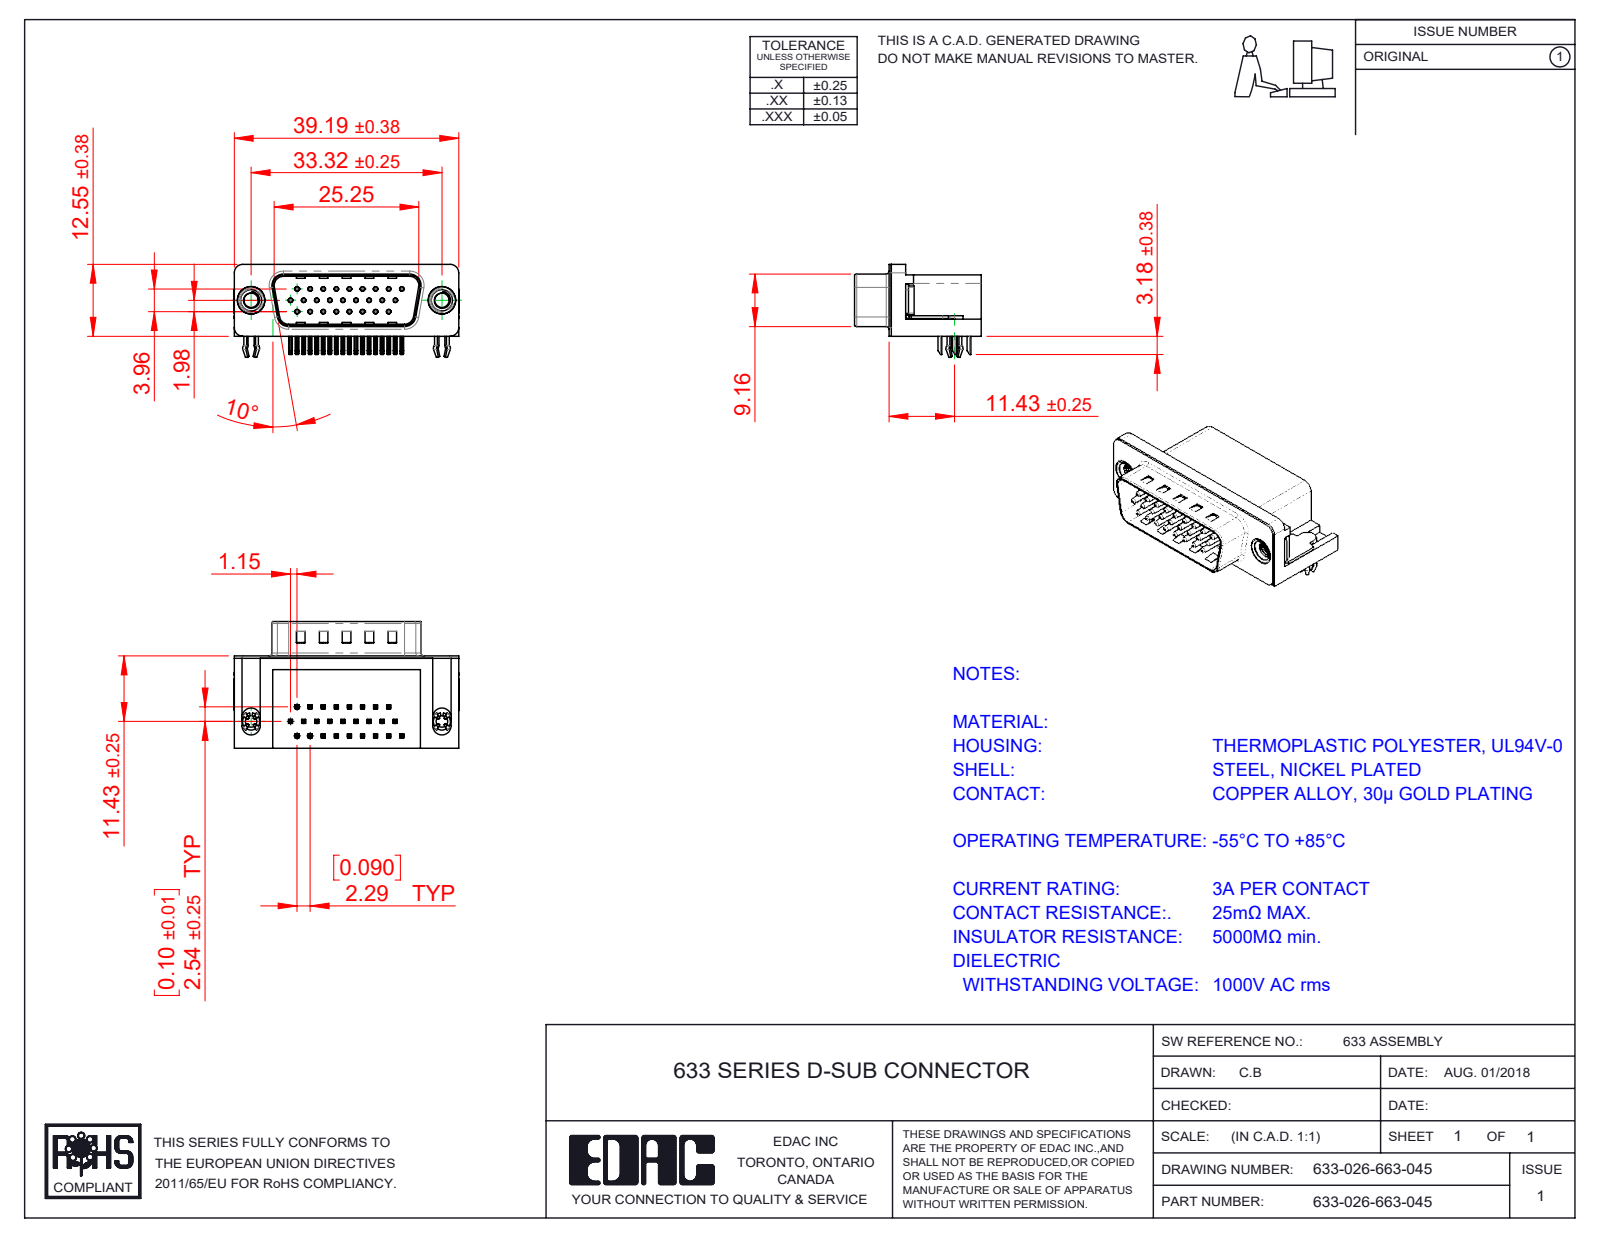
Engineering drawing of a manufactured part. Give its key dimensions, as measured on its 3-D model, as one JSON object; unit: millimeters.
{"part_name": "633 Contact Bottom; 633 Housing_26 Contact; 633-026-663-045; 633 Contact Middle (+4 more)", "step_written_by": "SolidWorks 2016 (CONFIG_CONTROL_DESIGN)", "units": "millimeters", "bodies": {"solids": 32, "faces": 2424, "planar": 1463, "cylindrical": 688, "other": 273}, "overall_size": [39.22, 22.1, 16.25], "volume_mm3": 5602, "surface_area_mm2": 7328, "round_holes": [[0.35, 26], [0.8, 26], [2, 2], [2.5, 2], [4, 2], [4.8, 2], [5, 2]], "round_bosses_or_shafts": [[0.75, 26], [4.9, 2], [4.75, 2], [3.9, 2], [3, 2]], "partial_cylinders_radius": [[0.25, 116], [0.12, 52], [1, 16], [0.5, 9], [1.5, 8], [1.6, 8], [0.9, 4], [2, 4]], "face_to_face_distances": [0.4, 10.35, 15.7, 2.9, 2.5, 16.1, 8.76, 0.35, 10.7, 0.5], "hole_center_spacings": [2.29, 4.57, 2.28, 3.96, 6.05, 4.58, 6.86, 7.92]}
